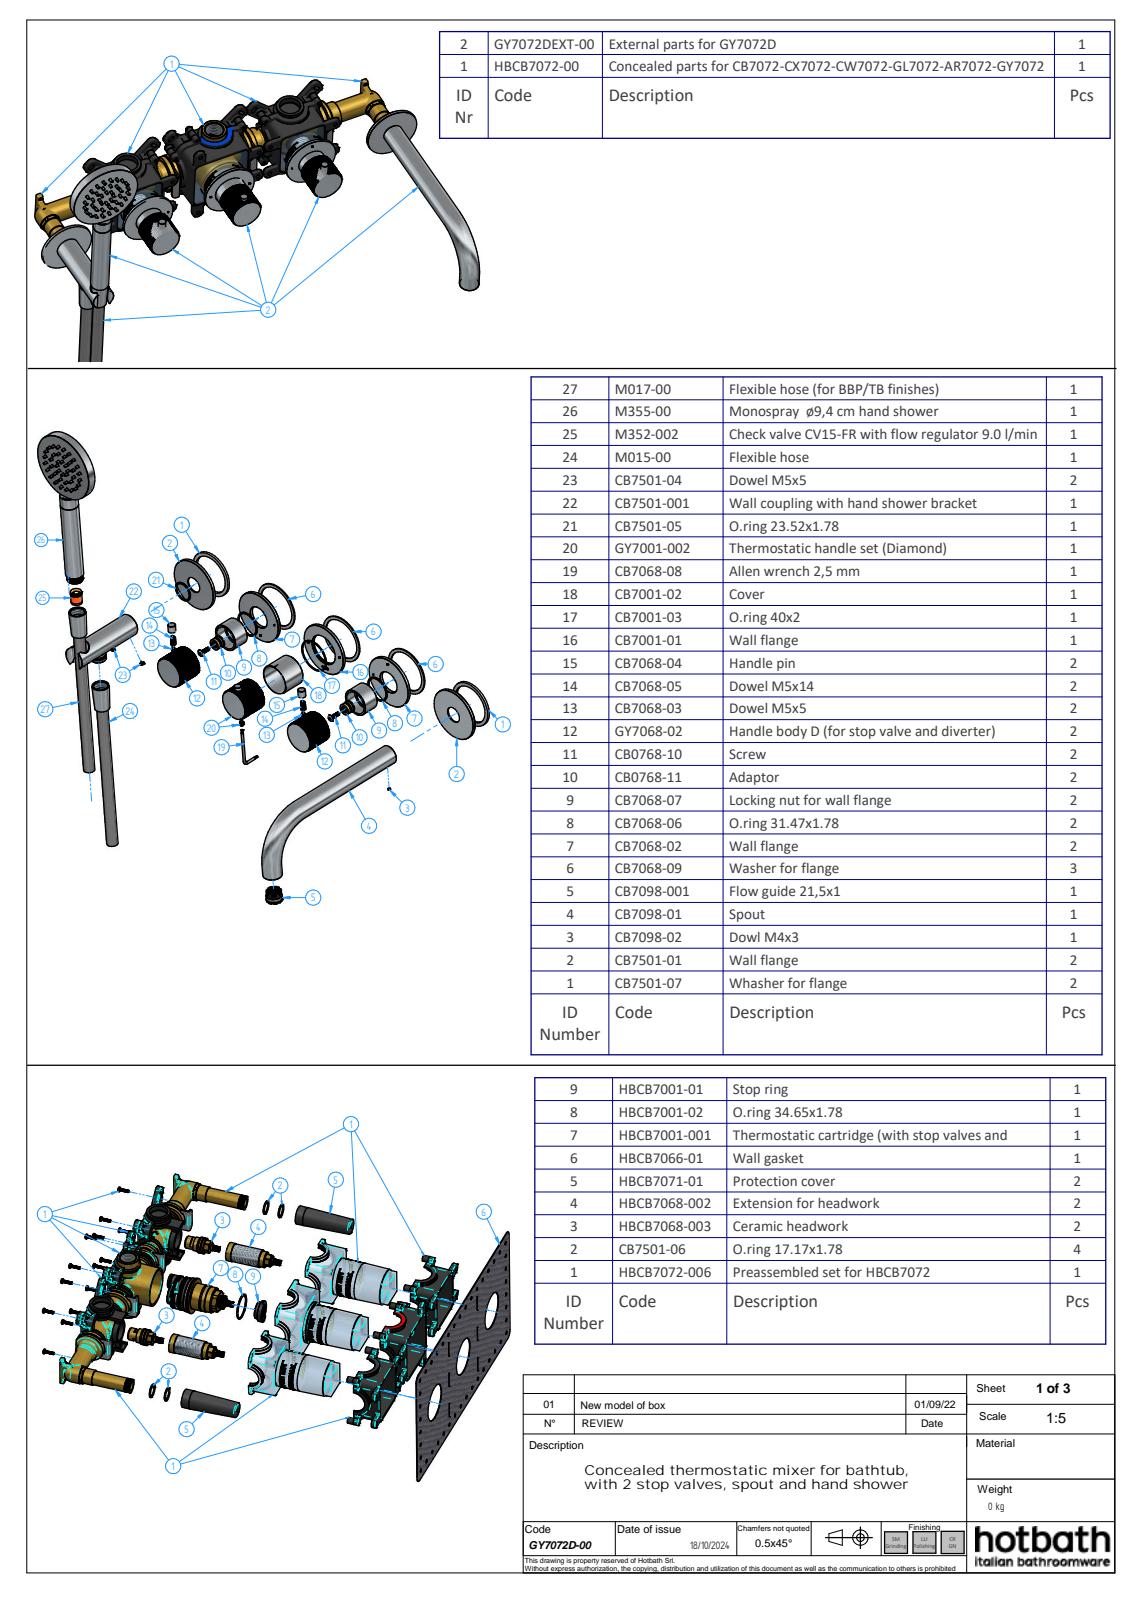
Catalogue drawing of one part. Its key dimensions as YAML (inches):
part_name: "GY7072DEXT-00; CB7098-01; CB7098-02; CB7098-001 (+8 more)"
step_written_by: "Solid Edge (AUTOMOTIVE_DESIGN)"
units: inches
bodies: {solids: 52, faces: 14225, planar: 5766, cylindrical: 2919, other: 5540}
overall_size: [22.165, 19.754, 10.165]
volume: 29.05
surface_area: 412.2
round_holes:
  - {diameter: 0.028, count: 40}
  - {diameter: 0.163, count: 5}
  - {diameter: 0.205, count: 3}
  - {diameter: 0.598, count: 3}
  - {diameter: 1.496, count: 3}
  - {diameter: 2.244, count: 3}
  - {diameter: 2.638, count: 3}
  - {diameter: 0.157, count: 2}
  - {diameter: 0.177, count: 2}
  - {diameter: 0.413, count: 2}
  - {diameter: 0.65, count: 2}
  - {diameter: 0.733, count: 2}
round_bosses_or_shafts:
  - {diameter: 2.835, count: 5}
  - {diameter: 0.197, count: 5}
  - {diameter: 2.598, count: 3}
  - {diameter: 0.394, count: 3}
  - {diameter: 0.157, count: 3}
  - {diameter: 2.52, count: 2}
  - {diameter: 2.047, count: 2}
  - {diameter: 1.024, count: 2}
partial_cylinders:
  - {radius: 0.177, count: 12}
  - {radius: 0.008, count: 8}
  - {radius: 0.032, count: 6}
  - {radius: 0.374, count: 4}
  - {radius: 0.022, count: 2}
  - {radius: 0.029, count: 2}
  - {radius: 0.039, count: 2}
  - {radius: 0.083, count: 2}
face_to_face_distances: [0.059, 0.118, 0.079, 0.157, 0.394, 3.535, 3.378, 4.008, 3.85, 0.472]
hole_center_spacings: [1.481, 2.489, 0.394, 0.779, 2.039, 2.245, 1.144, 1.782]
